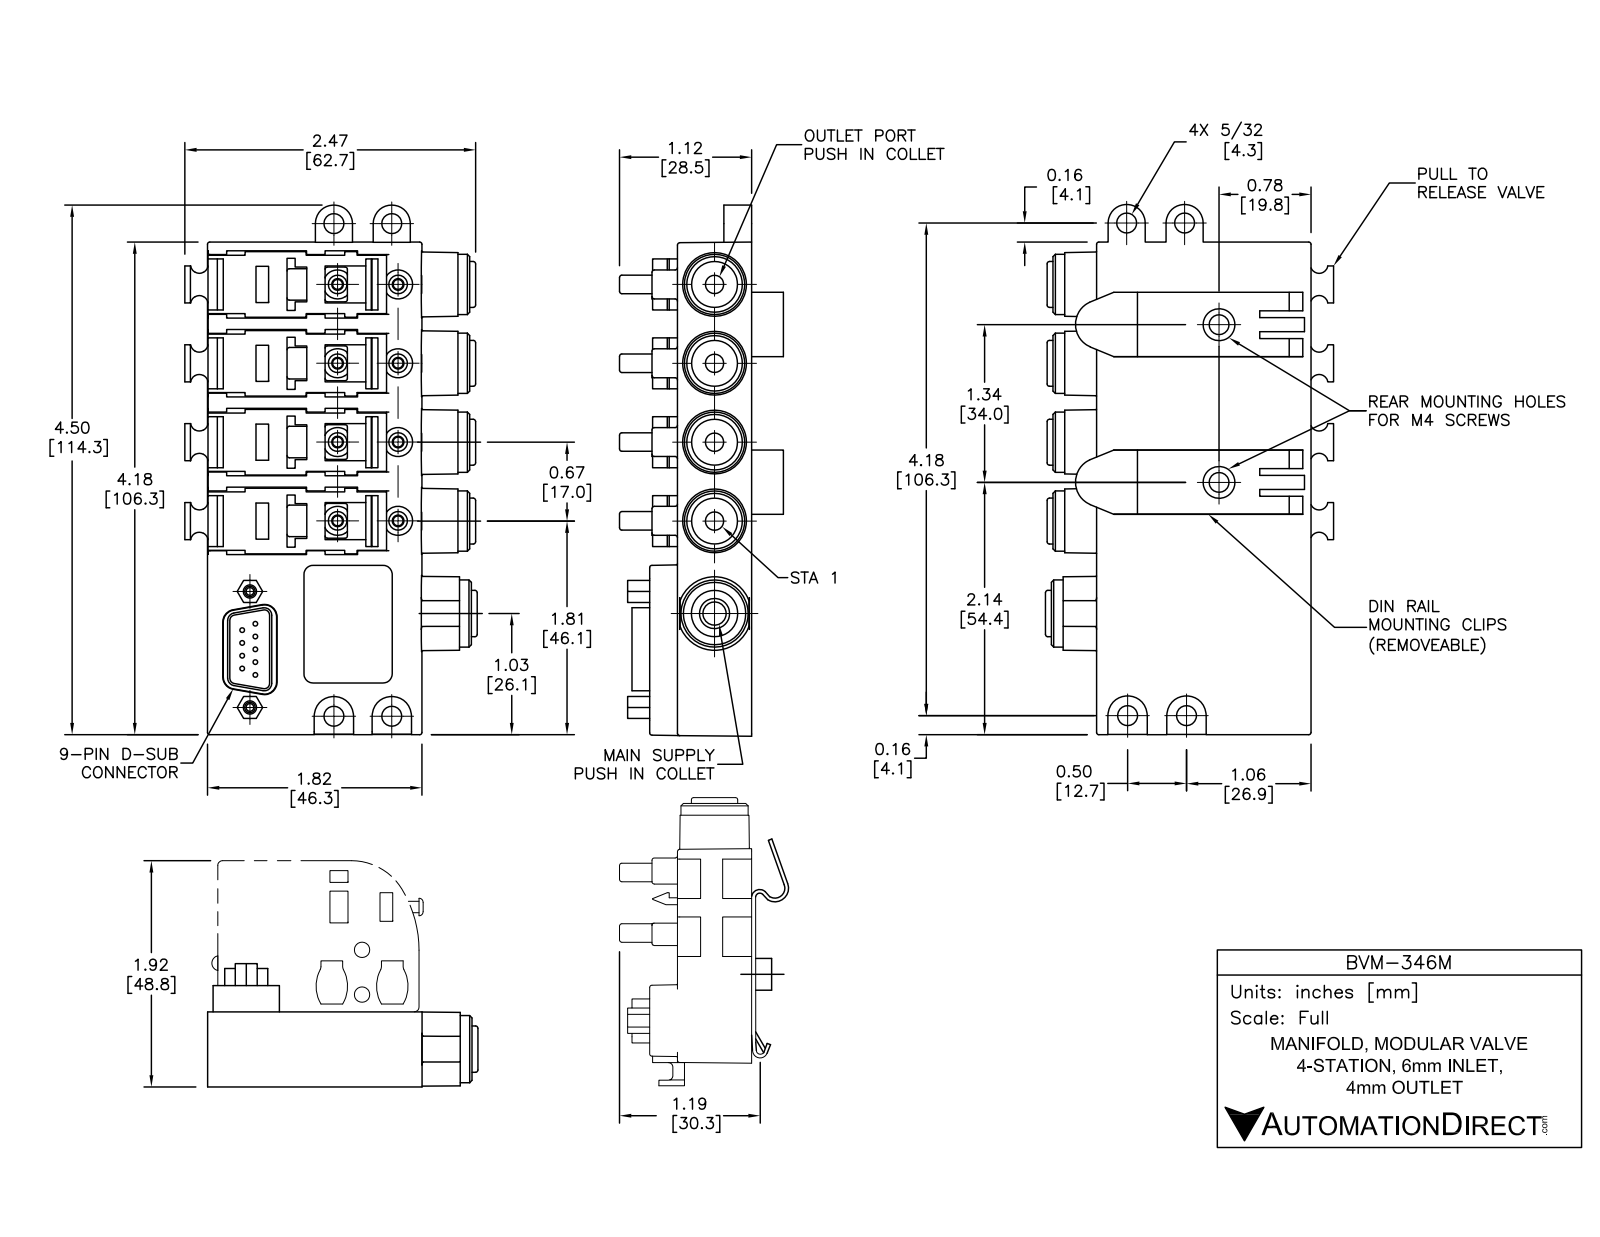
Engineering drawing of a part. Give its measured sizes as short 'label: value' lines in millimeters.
name: BVM-346M
written by: SolidWorks 2013 (AUTOMOTIVE_DESIGN)
unit: mm
bodies: 1 solid, 1123 faces (568 planar, 325 cylindrical, 230 other)
size: 114.27 × 62.17 × 28.5
volume: 87 375 mm³; area: 28 400 mm²
holes: 4× ⌀4.29, 3× ⌀3.94, 2× ⌀2.26, 1× ⌀3.94, 1× ⌀5, 1× ⌀6.5
bosses: 9× ⌀1, 8× ⌀4, 4× ⌀13, 4× ⌀9.91, 1× ⌀14.48, 1× ⌀10.01
rounds: 86× R0.5, 11× R0.25, 8× R0.15, 8× R1.9, 8× R3.12, 4× R1.14, 4× R1.6, 4× R2
face distances: 16, 0.5, 14.4, 1.6, 6, 15.5, 1.1, 6.5, 22, 7.6
hole spacings: 12.5, 17.02, 106.28, 107.01, 17.01, 18.22, 19.95, 25.02
